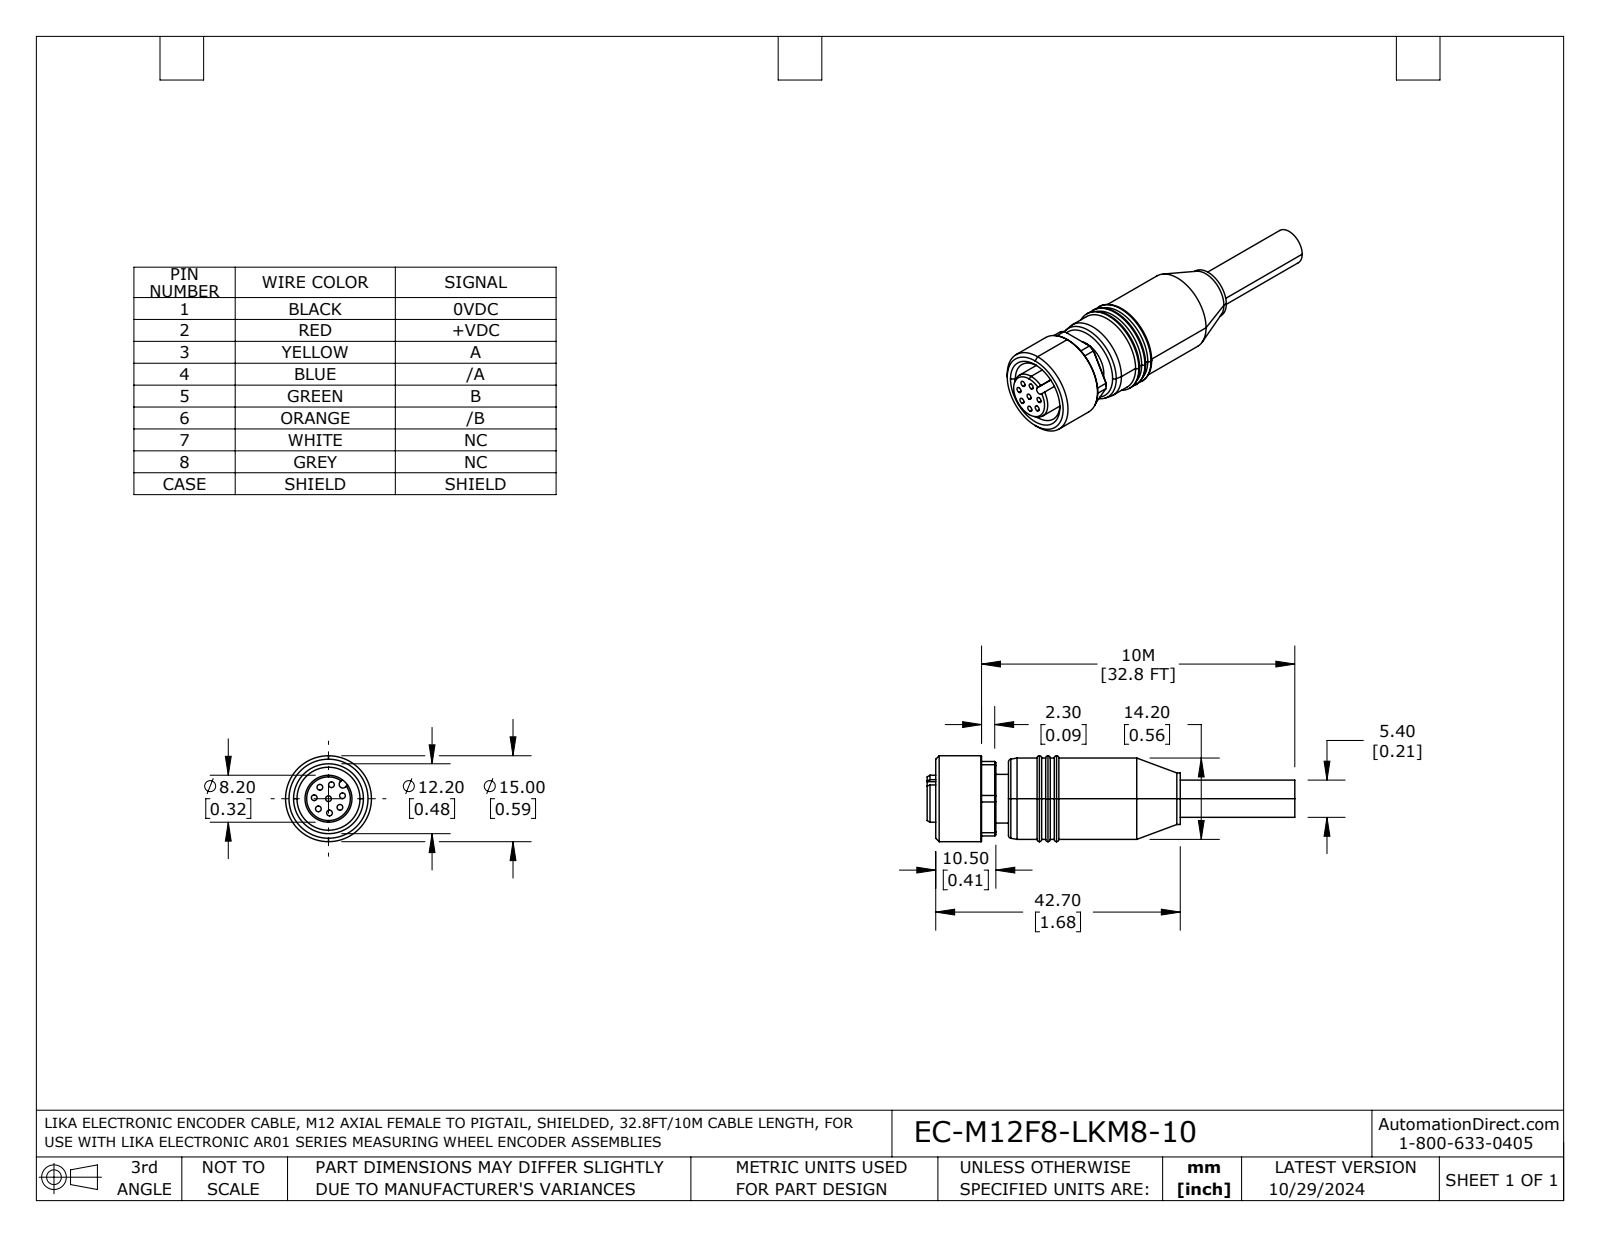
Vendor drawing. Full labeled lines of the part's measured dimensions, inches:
Part name (STEP PRODUCT): EC-M12F8-LKM8-10
STEP written by: SolidWorks 2021 (AUTOMOTIVE_DESIGN)
Units: inches
Bodies: 1 solid, 113 faces (31 planar, 43 cylindrical, 39 other)
Overall size (bounding box): 2.528 × 0.591 × 0.591
Volume: 0.404 in³ · Surface area: 5.26 in²
Round holes (diameter × count): ⌀0.039 ×8, ⌀0.433 ×1
Round bosses / shafts (diameter × count): ⌀0.591 ×1, ⌀0.559 ×1, ⌀0.354 ×1, ⌀0.335 ×1, ⌀0.323 ×1, ⌀0.256 ×1
Partial cylindrical surfaces — rounded edges, fillets, slot ends (radius × count): R0.026 ×1, R0.283 ×1
Main face-to-face distances: 0.087, 0.512, 0.205, 0.118, 0.559, 0.472, 0.354, 1.969, 2.055, 2.173
Hole centre spacings: 0.098, 0.081, 0.149, 0.195, 0.082, 0.166, 0.189, 0.189
